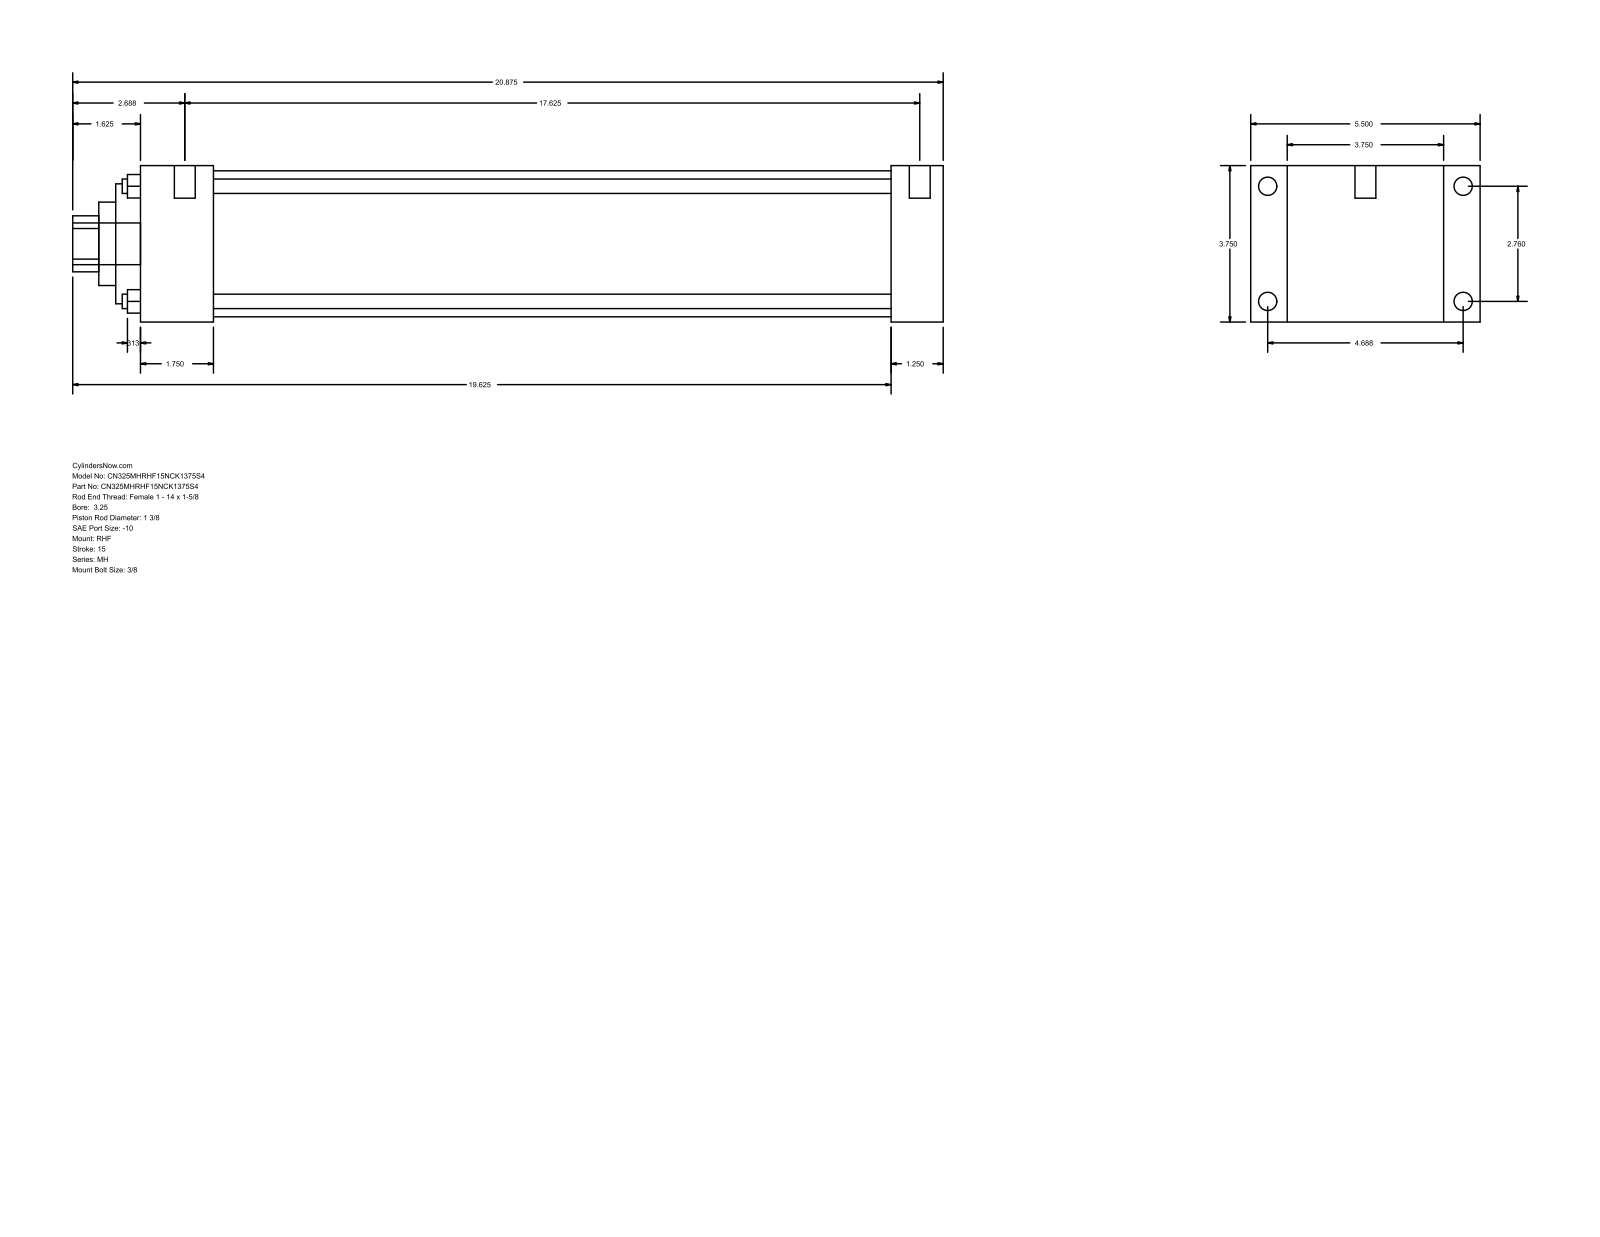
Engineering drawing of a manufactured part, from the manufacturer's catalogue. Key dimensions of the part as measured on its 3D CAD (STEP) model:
Part name (STEP PRODUCT): MH_RHF__0325_1.375
STEP written by: GSSL Pune (CONFIG_CONTROL_DESIGN)
Units: millimetres
Bodies: 0 solids, 90 faces (61 planar, 29 cylindrical, 0 other)
Overall size (bounding box): 530.23 × 139.7 × 95.25
Round holes (diameter × count): ⌀8.76 ×4, ⌀34.92 ×1, ⌀50.8 ×1, ⌀73.03 ×1, ⌀88.9 ×1
Round bosses / shafts (diameter × count): ⌀11.13 ×4, ⌀5.56 ×4, ⌀12.7 ×2, ⌀25.4 ×1
Partial cylindrical surfaces — rounded edges, fillets, slot ends (radius × count): R17.06 ×1
Main face-to-face distances: 95.24, 31.75, 22.23, 117.47, 457.21, 488.96, 139.7, 44.45, 412.76, 444.51
Hole centre spacings: 49.57, 70.1, 99.14
